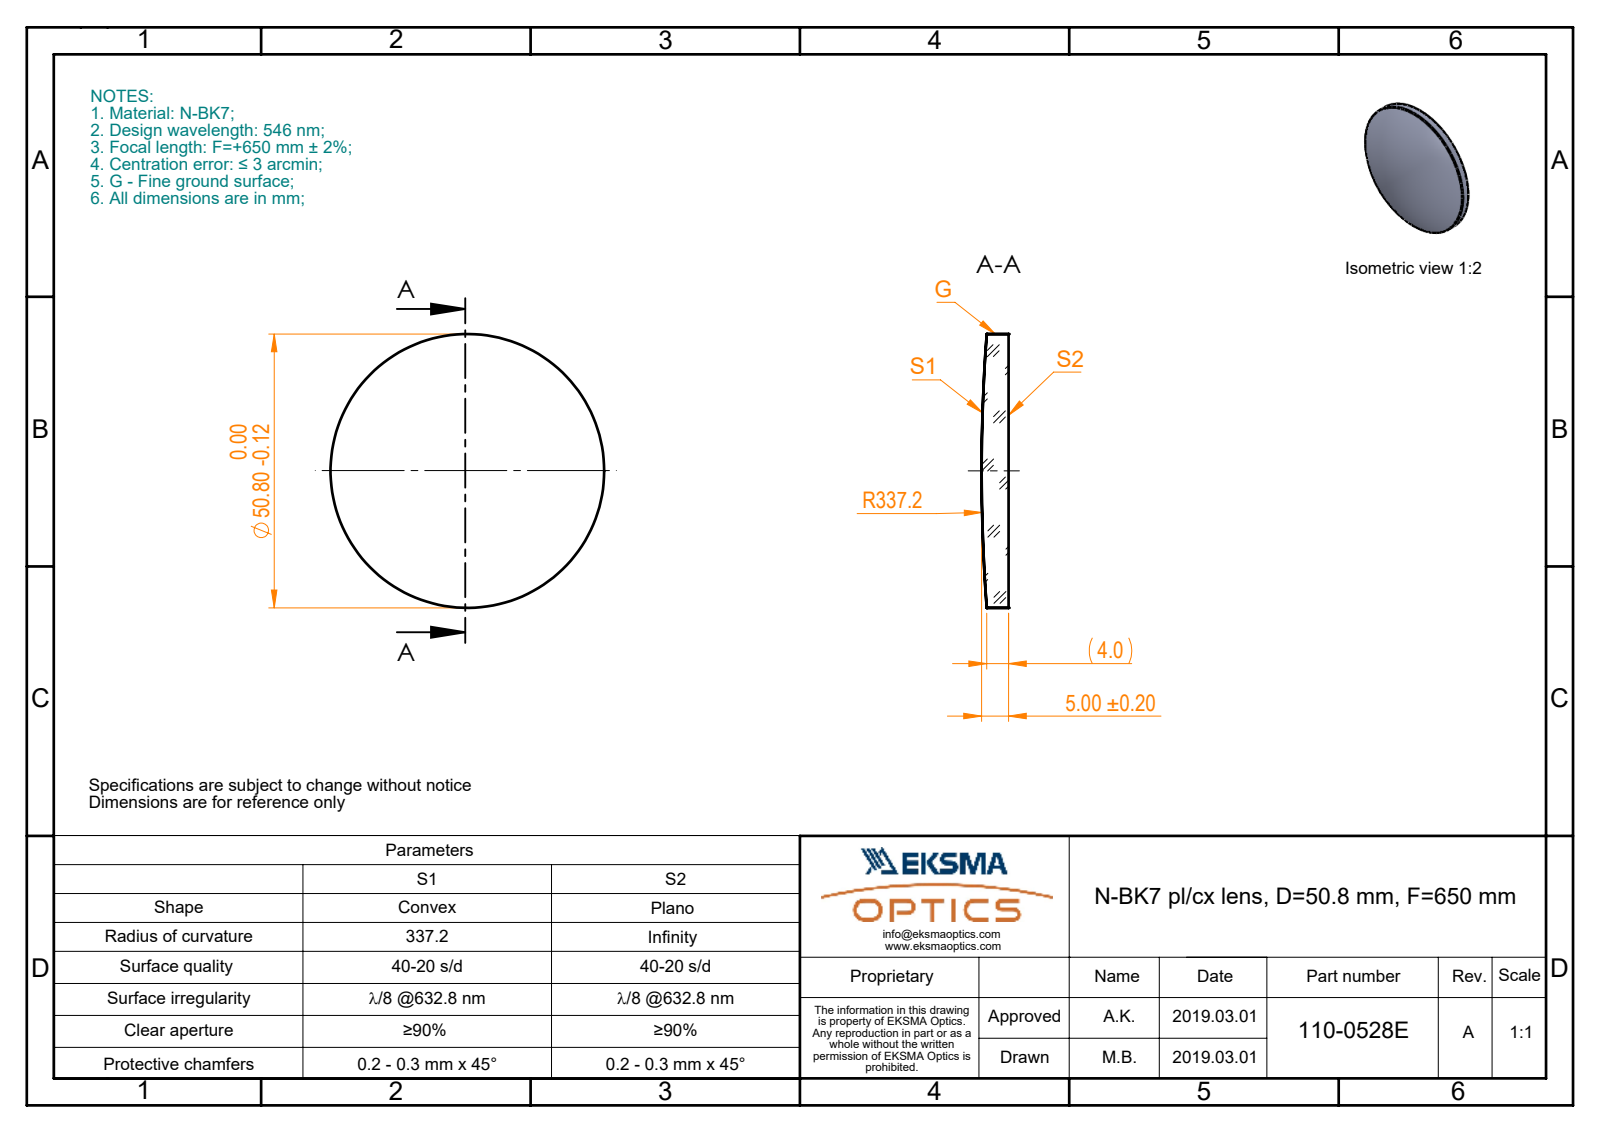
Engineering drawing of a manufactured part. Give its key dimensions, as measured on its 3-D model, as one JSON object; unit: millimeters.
{"part_name": "110-0528E BK7 pl-cx 50.8 F650", "step_written_by": "SolidWorks 2017 (CONFIG_CONTROL_DESIGN)", "units": "millimeters", "bodies": {"solids": 1, "faces": 5, "planar": 1, "cylindrical": 2, "other": 2}, "overall_size": [50.8, 50.8, 5], "volume_mm3": 9164, "surface_area_mm2": 4702, "round_bosses_or_shafts": [[50.8, 1]]}
